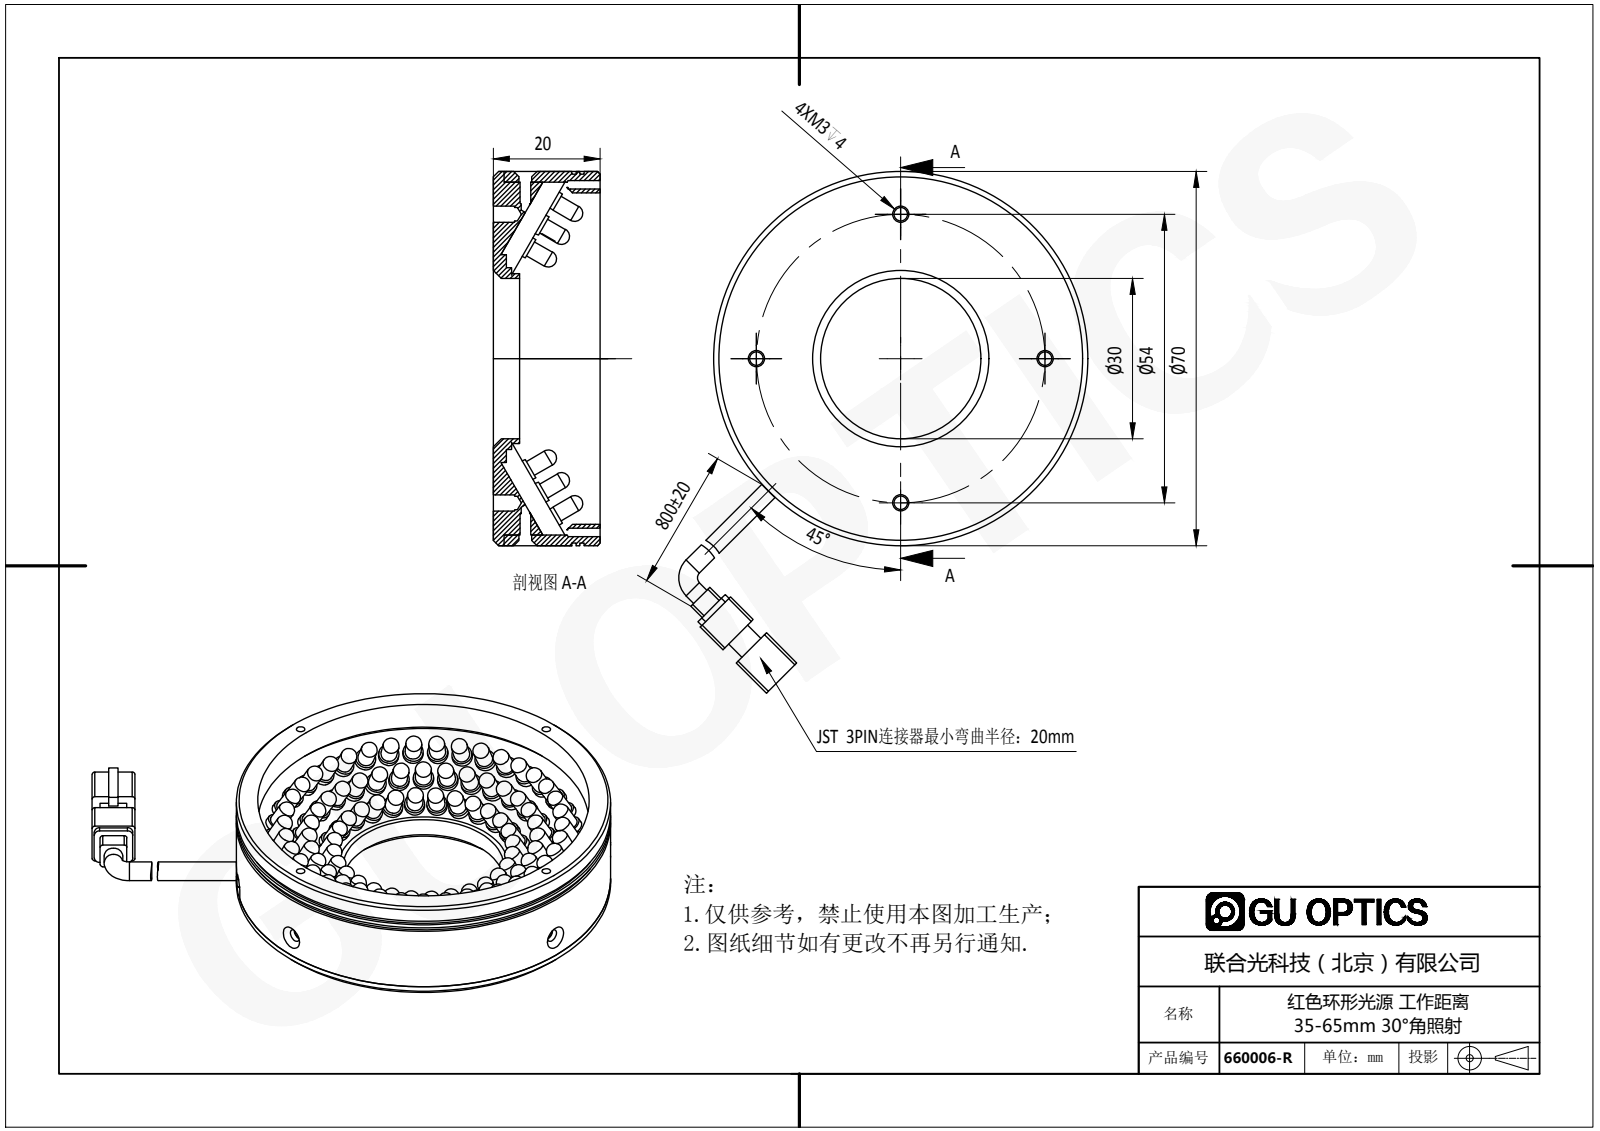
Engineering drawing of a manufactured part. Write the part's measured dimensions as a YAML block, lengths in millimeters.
part_name: "660006-R"
step_written_by: "SolidWorks 2016 (AUTOMOTIVE_DESIGN)"
units: millimeters
bodies: {solids: 103, faces: 1954, planar: 1269, cylindrical: 520, other: 165}
overall_size: [97.58, 76.52, 20.3]
volume: 29887
surface_area: 34722
round_holes:
  - {diameter: 3, count: 7}
  - {diameter: 1.6, count: 6}
  - {diameter: 2.5, count: 4}
  - {diameter: 2, count: 2}
  - {diameter: 2.4, count: 2}
  - {diameter: 30, count: 1}
  - {diameter: 62, count: 1}
round_bosses_or_shafts:
  - {diameter: 3.8, count: 98}
  - {diameter: 3, count: 96}
  - {diameter: 3.5, count: 2}
  - {diameter: 70, count: 1}
  - {diameter: 69, count: 1}
  - {diameter: 66, count: 1}
  - {diameter: 38.84, count: 1}
  - {diameter: 34, count: 1}
partial_cylinders:
  - {radius: 0.5, count: 8}
  - {radius: 1.6, count: 6}
  - {radius: 1, count: 4}
  - {radius: 9, count: 1}
face_to_face_distances: [2, 20, 18, 1, 0.5, 1.5, 3, 2.44, 0.44, 17.56]
hole_center_spacings: [42.25, 5.5, 27, 32.5, 38.18, 45.96, 59.5, 54]
